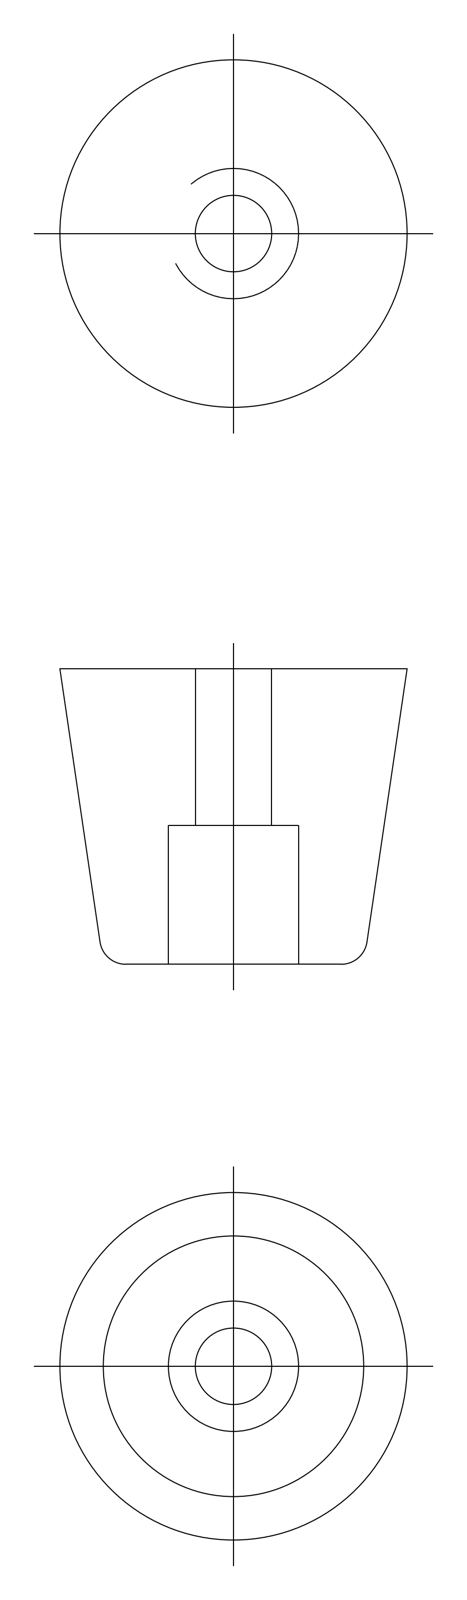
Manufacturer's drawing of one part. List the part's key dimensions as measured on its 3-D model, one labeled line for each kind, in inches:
STEP written by: spGate 19.8.4 (****-****-****-****) (AUTOMOTIVE_DESIGN)
Units: inches
Bodies: 1 solid, 11 faces (3 planar, 4 cylindrical, 4 other)
Overall size (bounding box): 0.787 × 0.787 × 0.669
Volume: 0.221 in³ · Surface area: 2.63 in²
Round holes (diameter × count): ⌀0.173 ×1, ⌀0.295 ×1
Main face-to-face distances: 0.669, 0.315, 0.354
